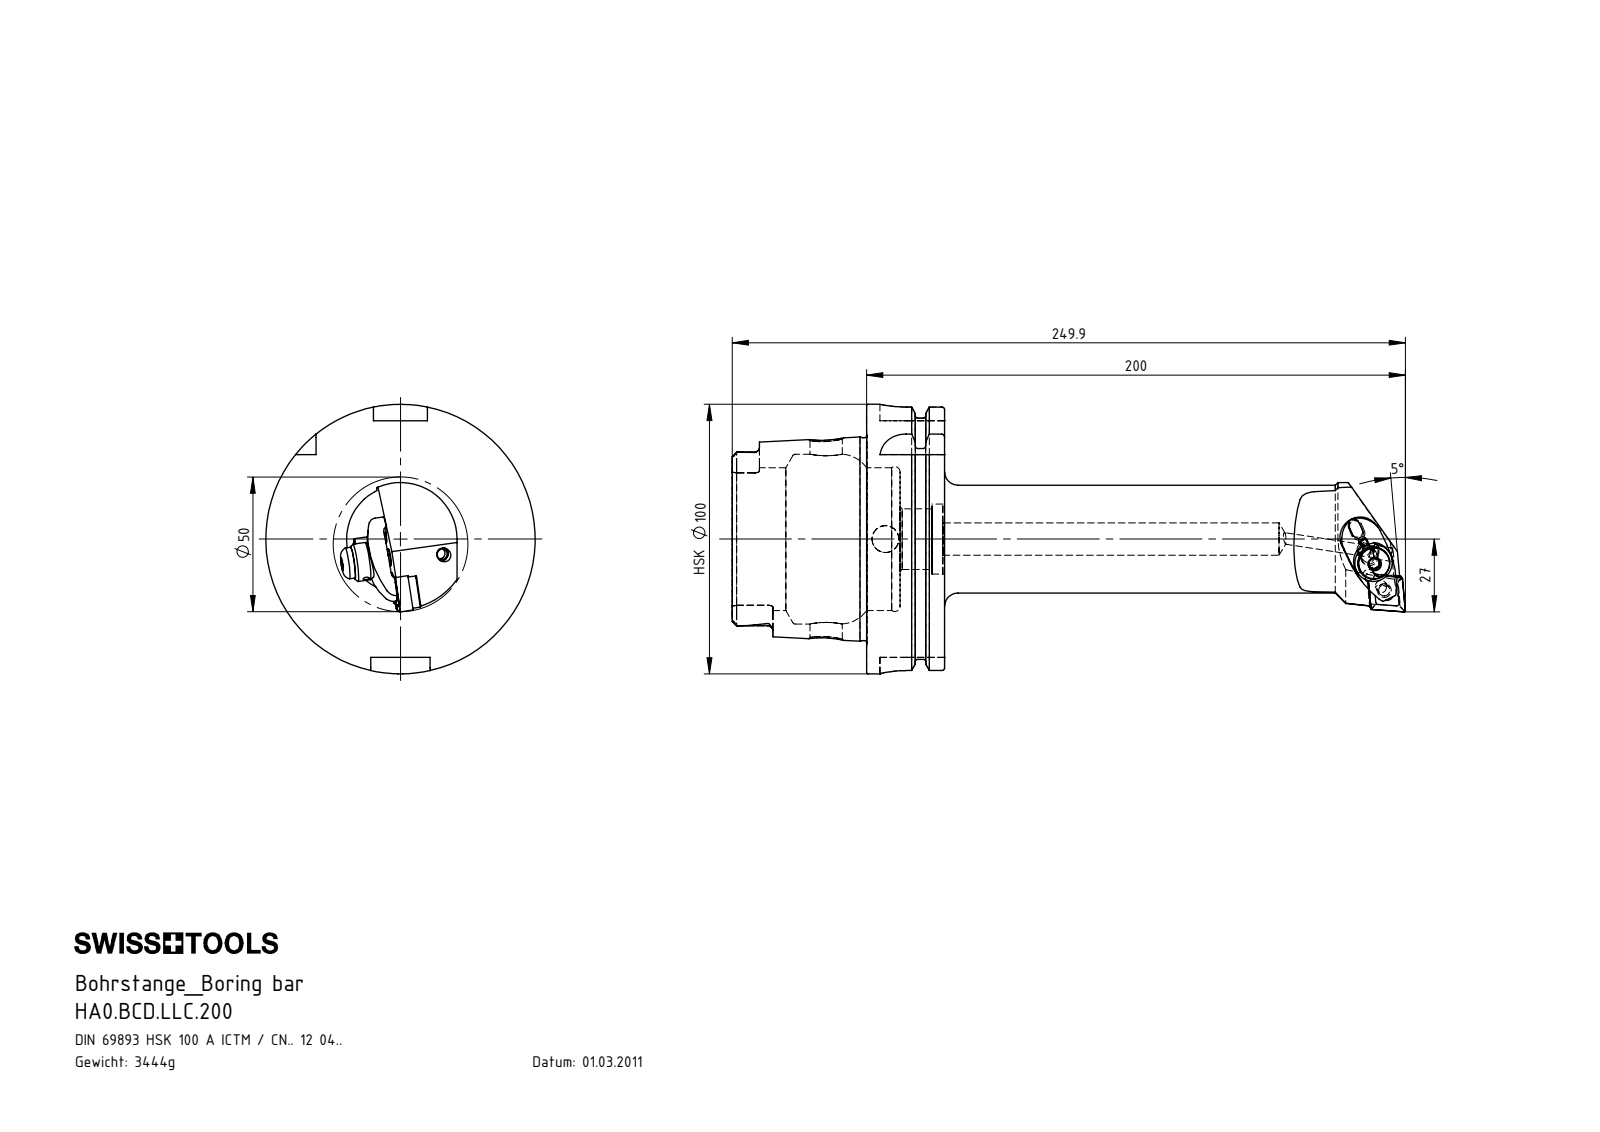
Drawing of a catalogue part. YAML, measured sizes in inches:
part_name: "HA0.BCD.LLC.200; WCC-ER5.102.012_B; HA0-BCD.LLC.200_B_Fertigbearbeitung; WCC-ER4.103.032_A (+6 more)"
step_written_by: "SolidWorks 2017 (AUTOMOTIVE_DESIGN)"
units: inches
bodies: {solids: 10, faces: 339, planar: 120, cylindrical: 103, other: 116}
overall_size: [9.839, 3.937, 3.937]
volume: 26.87
surface_area: 124.9
round_holes:
  - {diameter: 0.079, count: 3}
  - {diameter: 0.165, count: 3}
  - {diameter: 0.197, count: 2}
  - {diameter: 0.244, count: 2}
  - {diameter: 0.472, count: 2}
  - {diameter: 0.094, count: 1}
  - {diameter: 0.118, count: 1}
  - {diameter: 0.157, count: 1}
  - {diameter: 0.203, count: 1}
  - {diameter: 0.252, count: 1}
  - {diameter: 0.276, count: 1}
  - {diameter: 0.335, count: 1}
round_bosses_or_shafts:
  - {diameter: 0.197, count: 2}
  - {diameter: 0.118, count: 2}
  - {diameter: 3.937, count: 1}
  - {diameter: 3.62, count: 1}
  - {diameter: 2.963, count: 1}
  - {diameter: 1.575, count: 1}
  - {diameter: 0.551, count: 1}
  - {diameter: 0.453, count: 1}
partial_cylinders:
  - {radius: 0.015, count: 6}
  - {radius: 0.075, count: 6}
  - {radius: 0.016, count: 4}
  - {radius: 0.039, count: 4}
  - {radius: 0.394, count: 4}
  - {radius: 0.027, count: 3}
  - {radius: 0.027, count: 3}
  - {radius: 0.059, count: 3}
face_to_face_distances: [1.14, 0.49, 0.65, 1.965, 2.455, 3.104, 3.457, 3.079, 1.114, 0.624]
hole_center_spacings: [0.315, 0.315, 0.588, 0.591, 0.296, 0.304, 0.304, 0.323]
